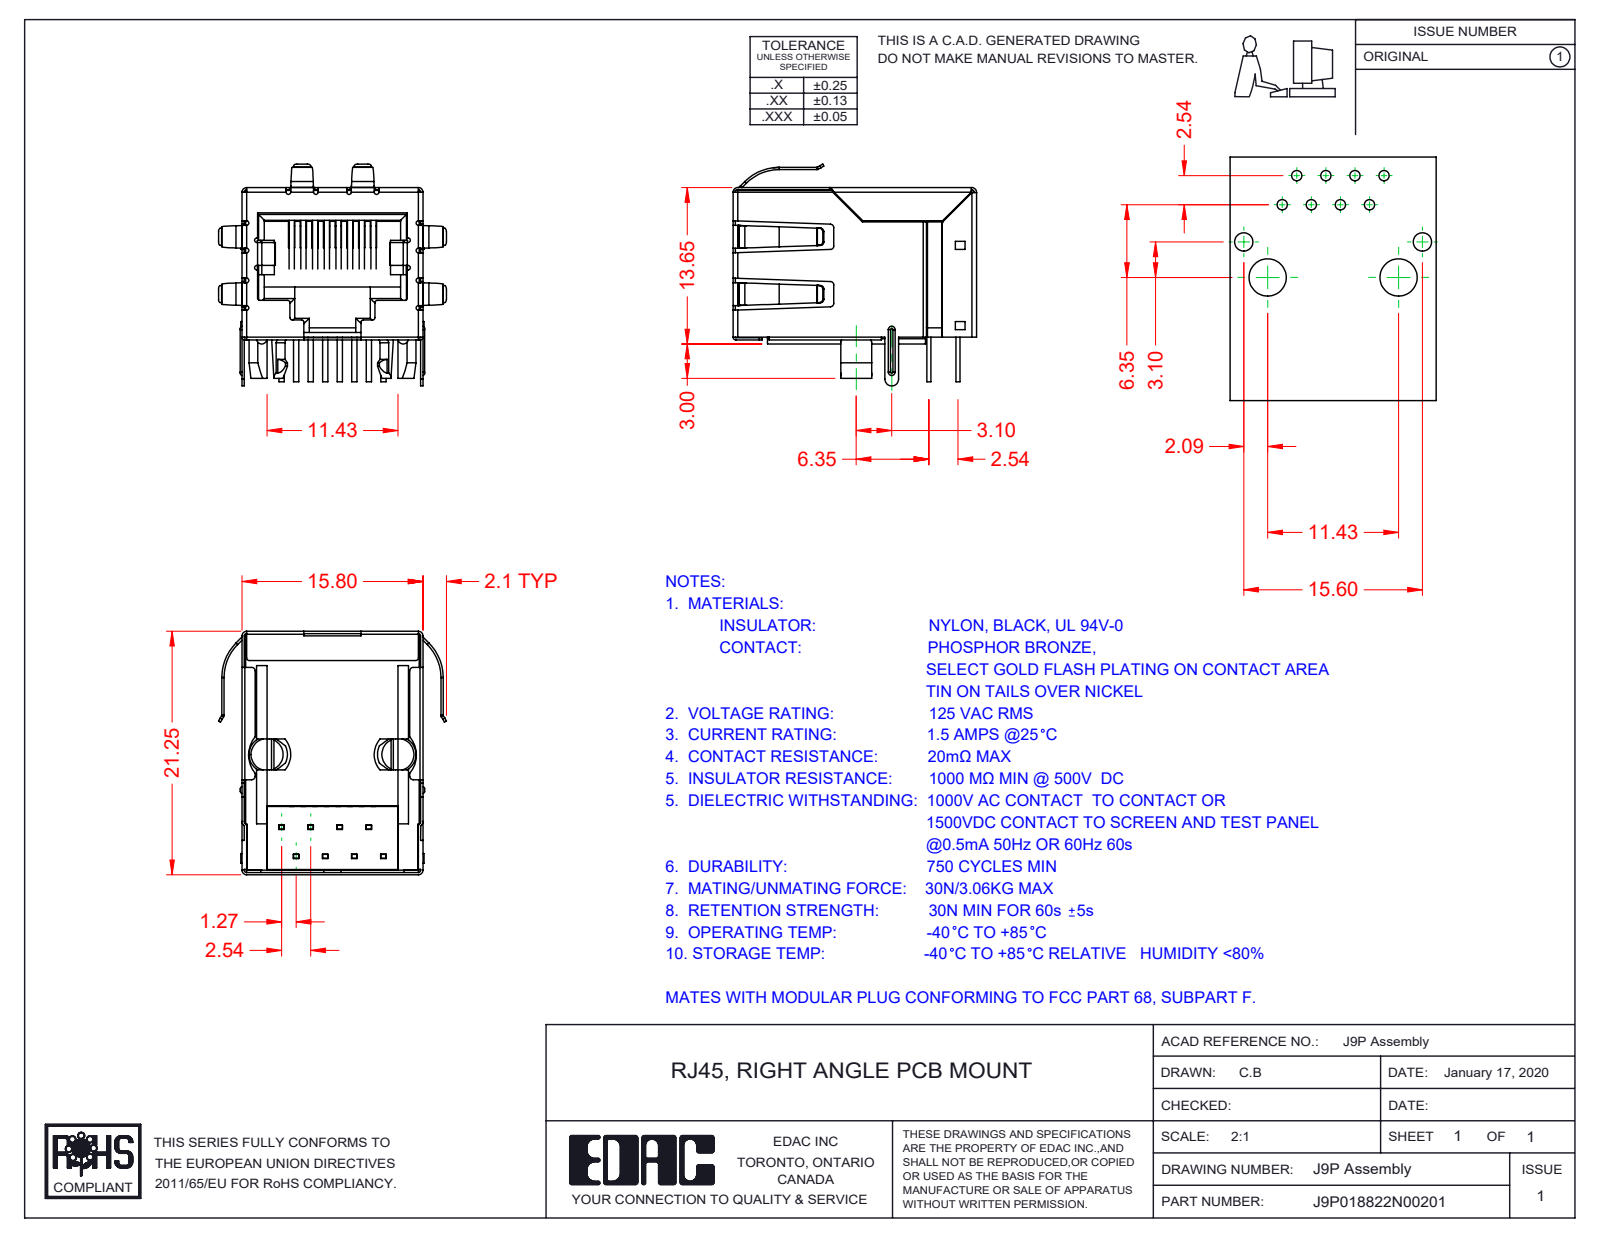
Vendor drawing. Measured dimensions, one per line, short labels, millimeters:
name: 9P-NOLED Contacts; J9P018822N00201; 9P-NOLED Insulator; 9P-NOLED Assembly (+2 more)
written by: SolidWorks 2016 (CONFIG_CONTROL_DESIGN)
unit: mm
bodies: 11 solids, 1313 faces (892 planar, 319 cylindrical, 102 other)
size: 21.25 × 19.9 × 19.36
volume: 2 583 mm³; area: 7 121 mm²
rounds: 42× R0.2, 24× R0.3, 13× R0.4, 13× R0.5, 5× R0.23, 5× R0.25, 3× R0.15, 3× R0.25
face distances: 0.8, 12.05, 15.6, 15.15, 12.85, 1, 15.4, 13.05, 12, 12.8
